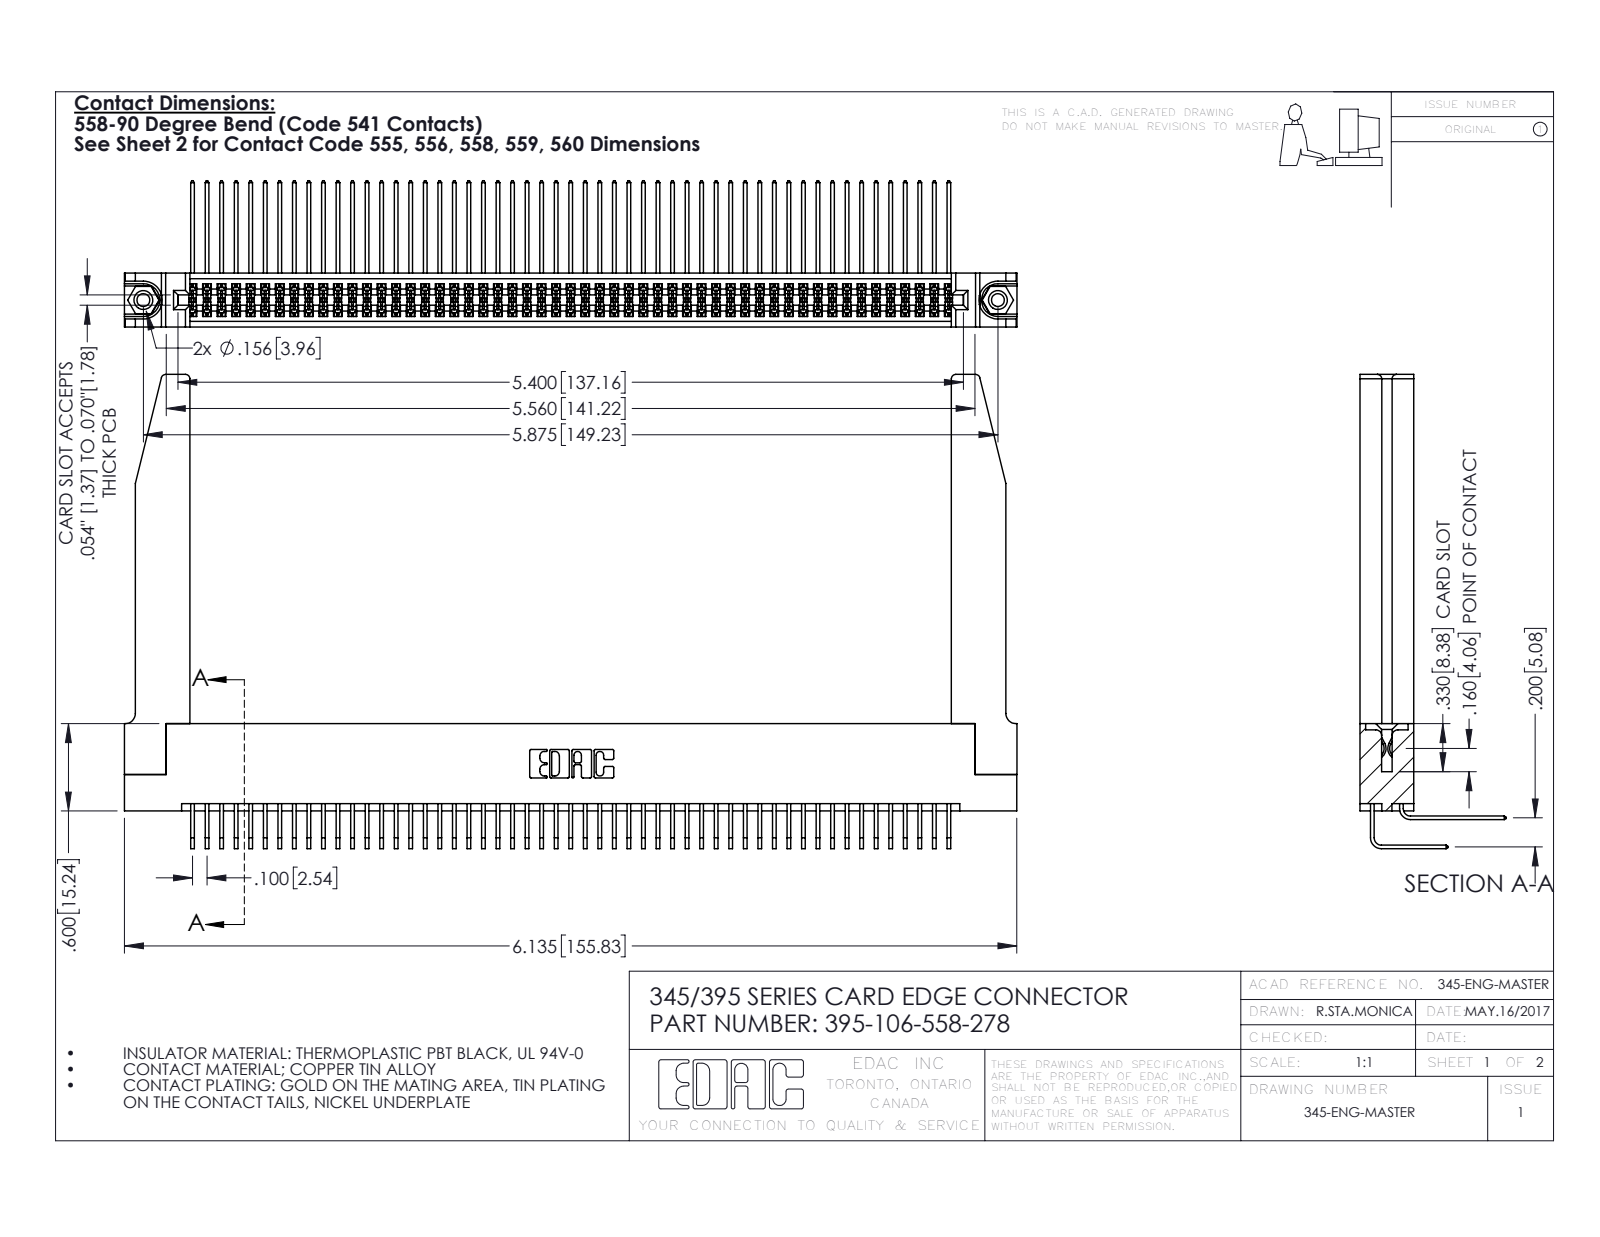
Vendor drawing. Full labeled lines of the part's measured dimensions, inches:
Part name (STEP PRODUCT): 345-292-001_558 Tail - 2; 345-292-001_558 559 Tail - 1; 345-250-001_345-250-001-102; 395-106-558-278 (+2 more)
STEP written by: SolidWorks 2016 (CONFIG_CONTROL_DESIGN)
Units: inches
Bodies: 111 solids, 5872 faces (3932 planar, 1888 cylindrical, 52 other)
Overall size (bounding box): 6.136 × 3.259 × 1.005
Volume: 1.442 in³ · Surface area: 51.71 in²
Round holes (diameter × count): ⌀0.089 ×2, ⌀0.125 ×2, ⌀0.156 ×2, ⌀0.064 ×1
Round bosses / shafts (diameter × count): ⌀0.155 ×2
Partial cylindrical surfaces — rounded edges, fillets, slot ends (radius × count): R0.006 ×160, R0.01 ×22, R0.03 ×8, R0.007 ×6, R0.031 ×6, R0.026 ×3, R0.014 ×2, R0.019 ×2
Main face-to-face distances: 0.072, 0.298, 0.37, 0.2, 0.098, 0.272, 0.025, 0.225, 0.285, 0.025
Hole centre spacings: 0.27, 5.639, 5.875
